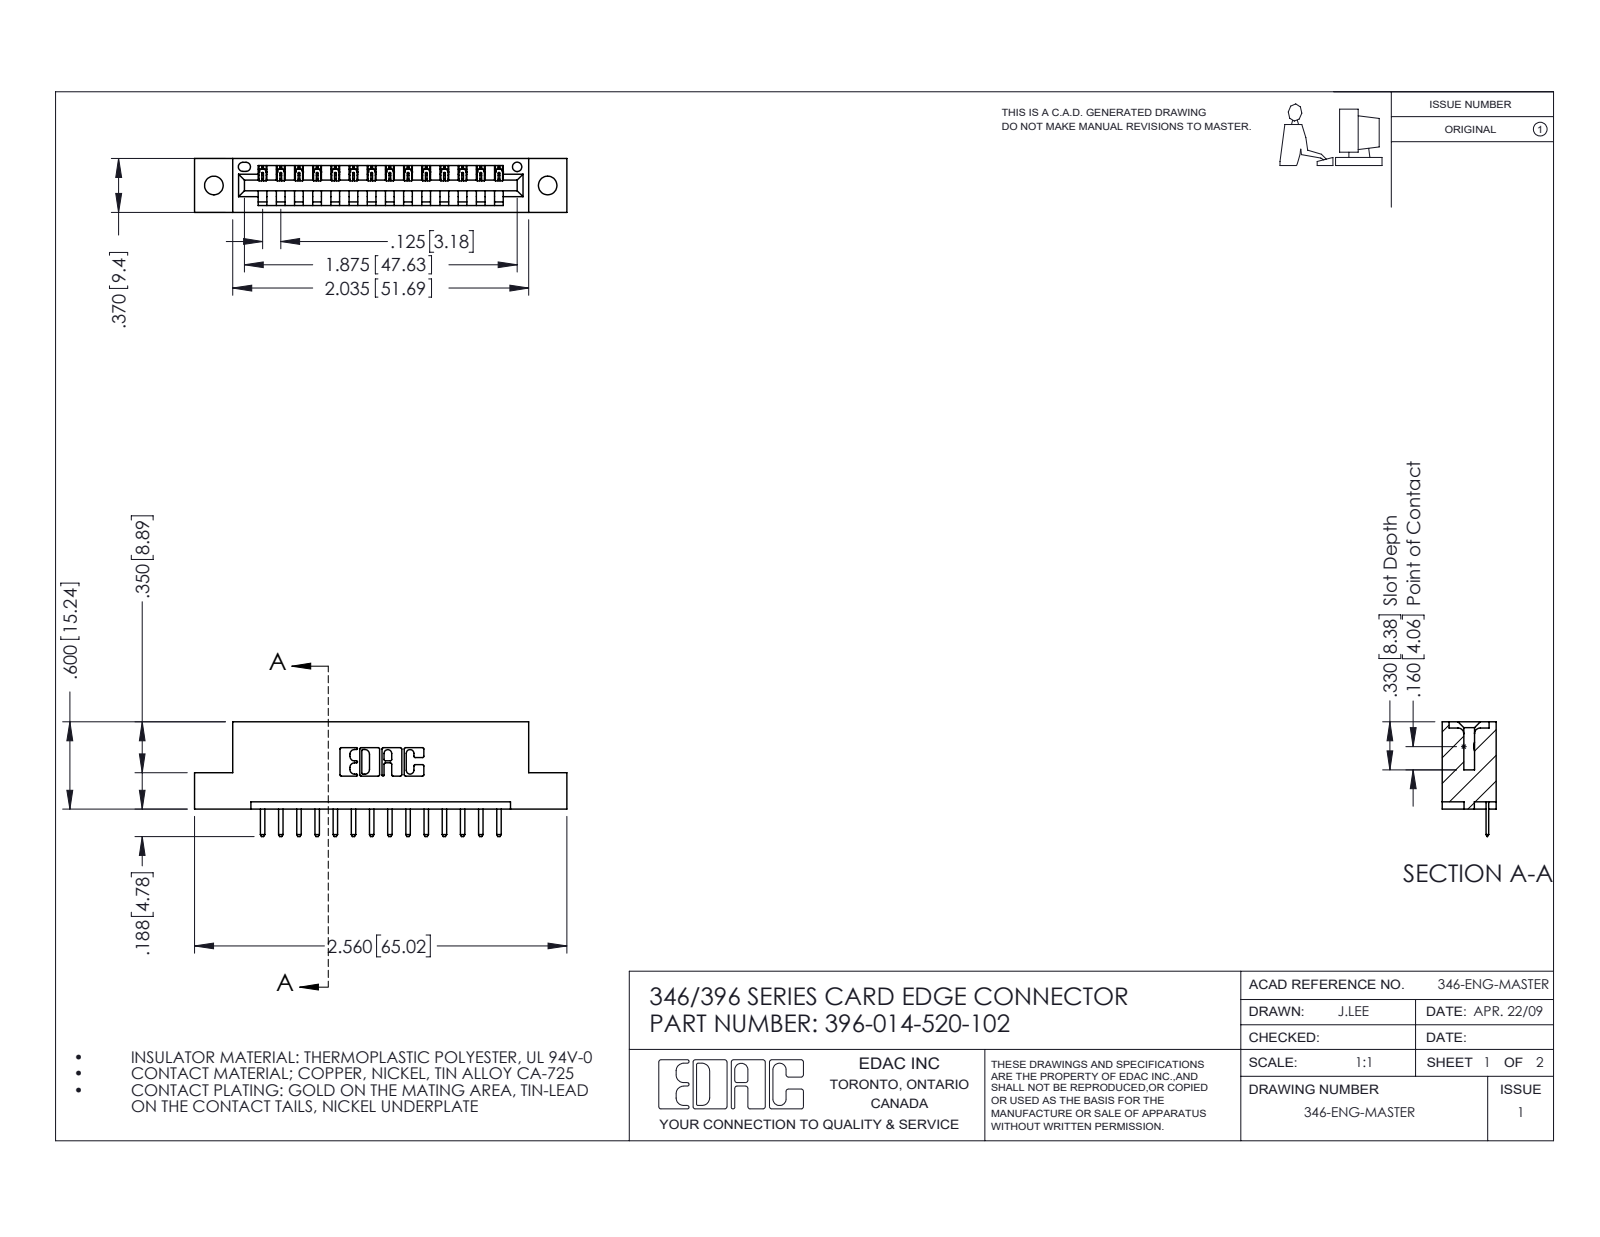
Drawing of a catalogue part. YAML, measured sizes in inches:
part_name: "346 Part_Flush Mounting Lugs - 0.128 Dia; 345-292-001_345-293-120; 396-014-520-102"
step_written_by: "SolidWorks 2016 (CONFIG_CONTROL_DESIGN)"
units: inches
bodies: {solids: 15, faces: 990, planar: 664, cylindrical: 326, other: 0}
overall_size: [2.56, 0.788, 0.37]
volume: 0.363
surface_area: 10.44
round_holes:
  - {diameter: 0.128, count: 2}
  - {diameter: 0.064, count: 1}
partial_cylinders:
  - {radius: 0.01, count: 30}
  - {radius: 0.006, count: 28}
  - {radius: 0.01, count: 22}
  - {radius: 0.007, count: 6}
  - {radius: 0.031, count: 6}
  - {radius: 0.026, count: 3}
  - {radius: 0.031, count: 2}
  - {radius: 0.04, count: 2}
face_to_face_distances: [0.25, 0.37, 0.048, 0.322, 0.148, 0.222, 0.1, 0.174, 0.072, 0.298]
hole_center_spacings: [0.246, 2.089, 2.295]
